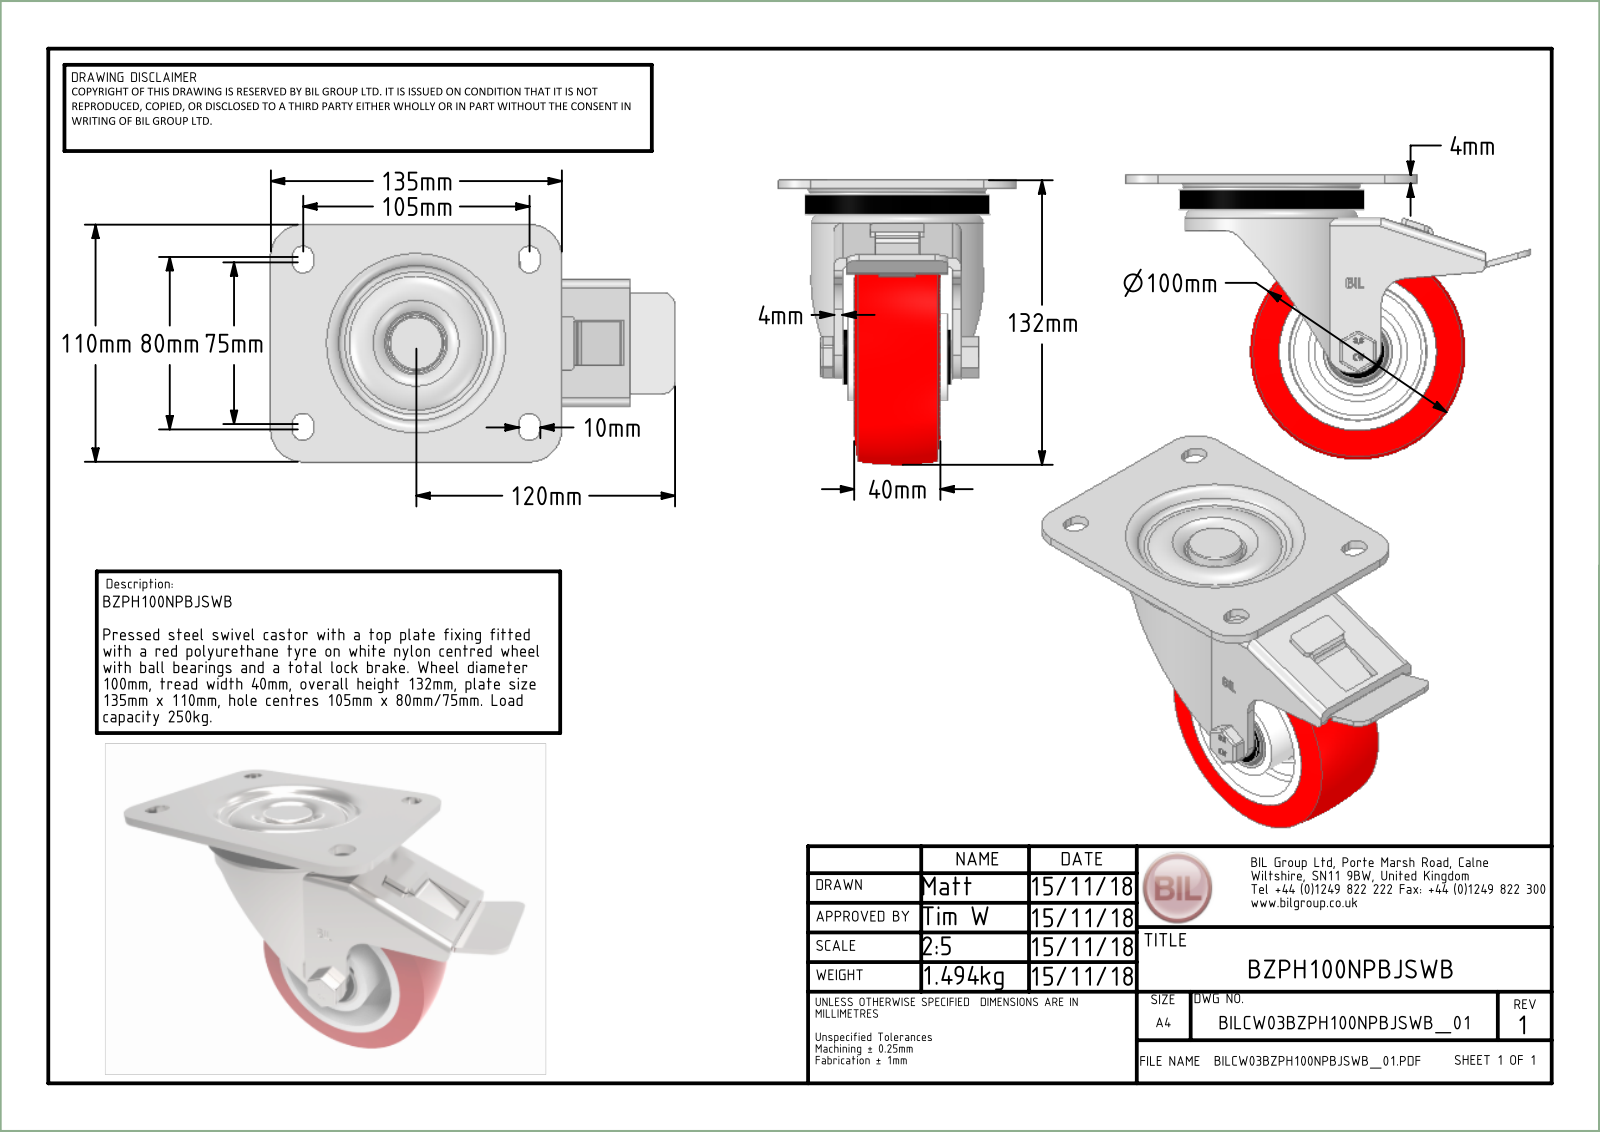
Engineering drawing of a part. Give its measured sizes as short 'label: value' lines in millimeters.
name: BZPH100NPBJSWB v3; BZPH100ASSWB - 52 v1; ZINC PLATED, PRESSED STEEL TOP PLATE; ZINC PLATED, PRESSED STEEL FORKS (+8 more)
written by: Autodesk Translation Framework v14.10.0.0 (AUTOMOTIVE_DESIGN)
unit: mm
bodies: 44 solids, 1401 faces (614 planar, 255 cylindrical, 532 other)
size: 187.5 × 132 × 110
volume: 415 642 mm³; area: 184 497 mm²
holes: 2× ⌀28, 1× ⌀8, 1× ⌀10, 1× ⌀10.2, 1× ⌀10.5, 1× ⌀12, 1× ⌀15, 1× ⌀15.75, 1× ⌀20.5, 1× ⌀26, 1× ⌀26.8, 1× ⌀28.2
bosses: 2× ⌀25, 1× ⌀83.5, 1× ⌀80, 1× ⌀60, 1× ⌀51, 1× ⌀40, 1× ⌀32, 1× ⌀21.5
rounds: 27× R0.5, 15× R2, 10× R0.75, 10× R4, 8× R5.5, 7× R1.5, 4× R1.25, 4× R3
face distances: 4, 9, 6, 13, 50, 2, 10, 46, 40, 56
